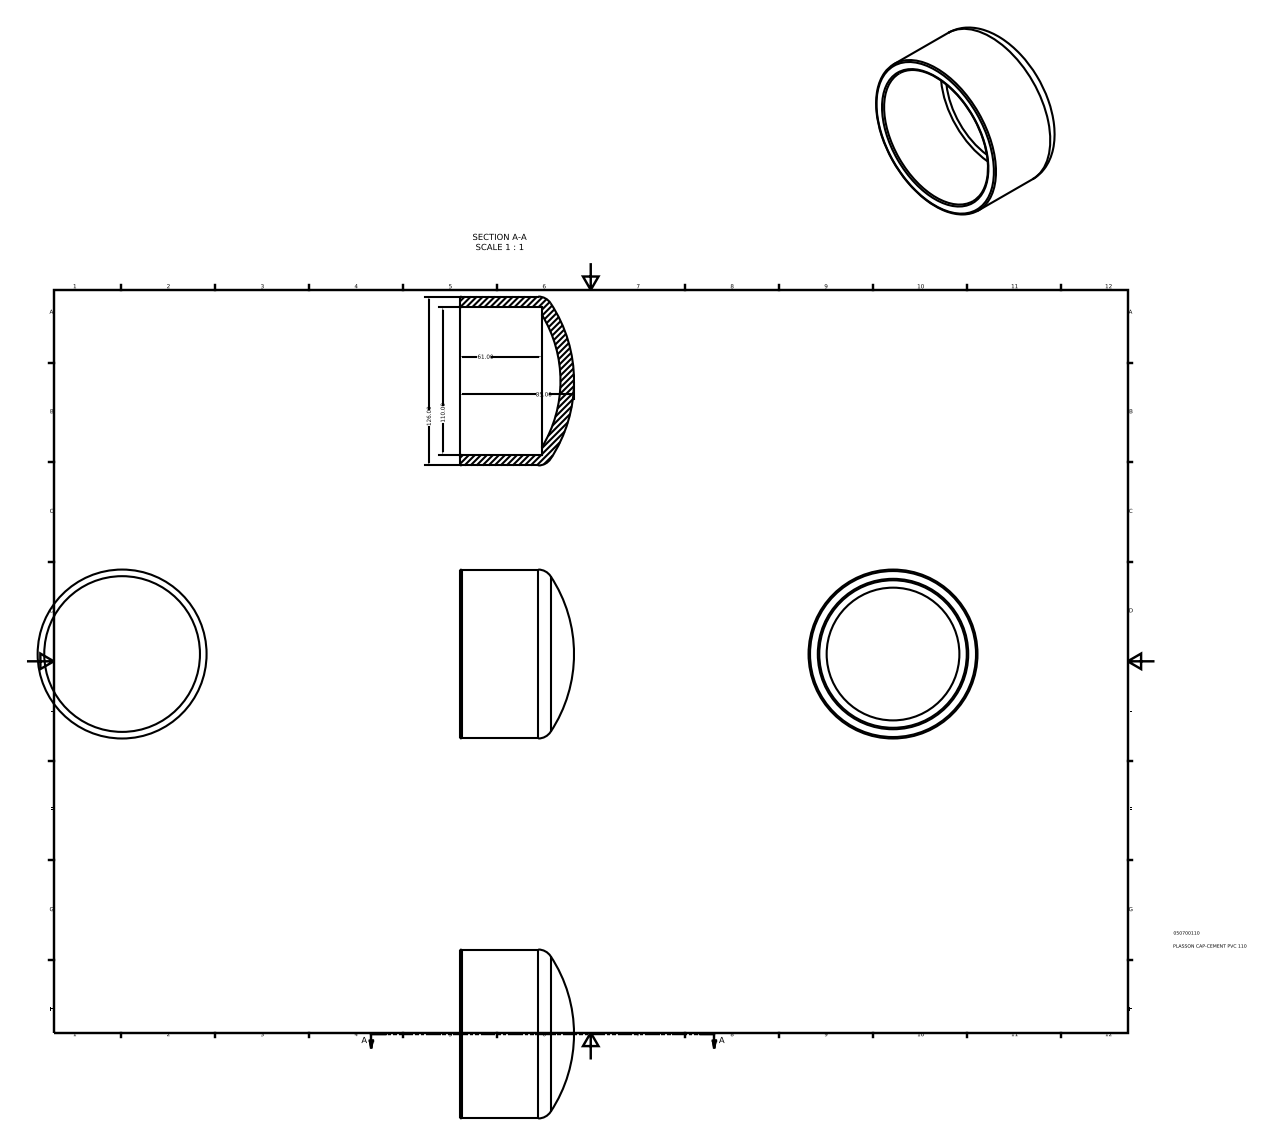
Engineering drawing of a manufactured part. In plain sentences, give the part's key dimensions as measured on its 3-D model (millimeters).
The part is named "050700110". Its 3-D file was written by "Autodesk Inventor 2015 (AUTOMOTIVE_DESIGN)". It is 1 solid with 9 faces: 2 planar, 2 cylindrical and 5 other. Overall it measures 126 by 126 by 85 millimeters. Its volume is 297 313 cubic millimeters and its surface area 72 634 square millimeters. Round holes: 1 of diameter 110. Round bosses or shafts: 1 of diameter 126. The main face-to-face distances are 61.
